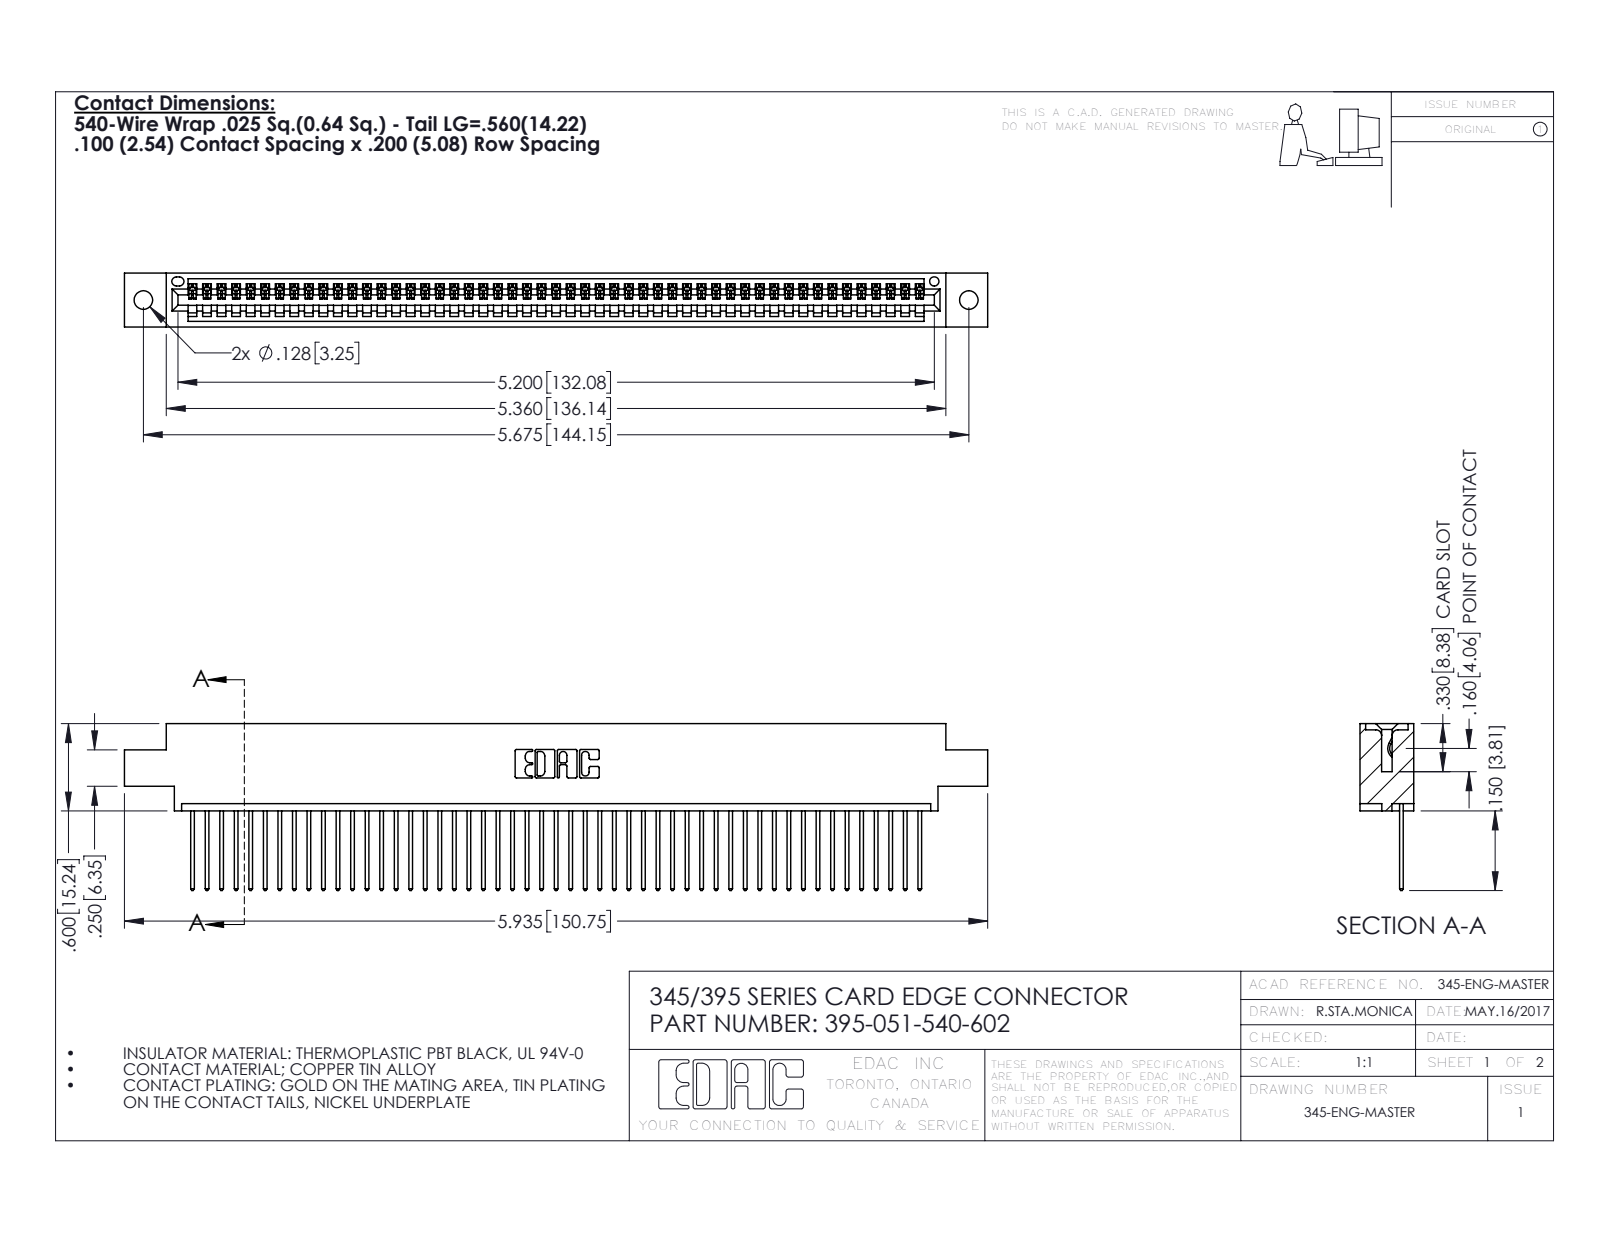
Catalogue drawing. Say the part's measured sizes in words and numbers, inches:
The part is named "395-051-540-602; 345-292-001_345-293-140; 345 Part_0.170 Offset - 0.128 Dia". Its 3-D file was written by "SolidWorks 2016 (CONFIG_CONTROL_DESIGN)". It is 52 solids with 3088 faces: 2124 planar, 964 cylindrical and 0 other. Overall it measures 5.935 by 1.147 by 0.37 inches. Its volume is 0.873 cubic inches and its surface area 30.21 square inches. Round holes: 2 of diameter 0.128, 1 of diameter 0.064. Partial cylindrical surfaces (rounded edges, fillets, slot ends): 102 of radius 0.006, 102 of radius 0.01, 22 of radius 0.01, 6 of radius 0.007, 6 of radius 0.031, 3 of radius 0.026, 2 of radius 0.031, 2 of radius 0.04. The main face-to-face distances are 0.298, 0.072, 0.37, 0.098, 0.272, 0.025, 0.2, 0.225, 0.175, 0.149. The hole center spacings are 0.27, 5.439, 5.675.
